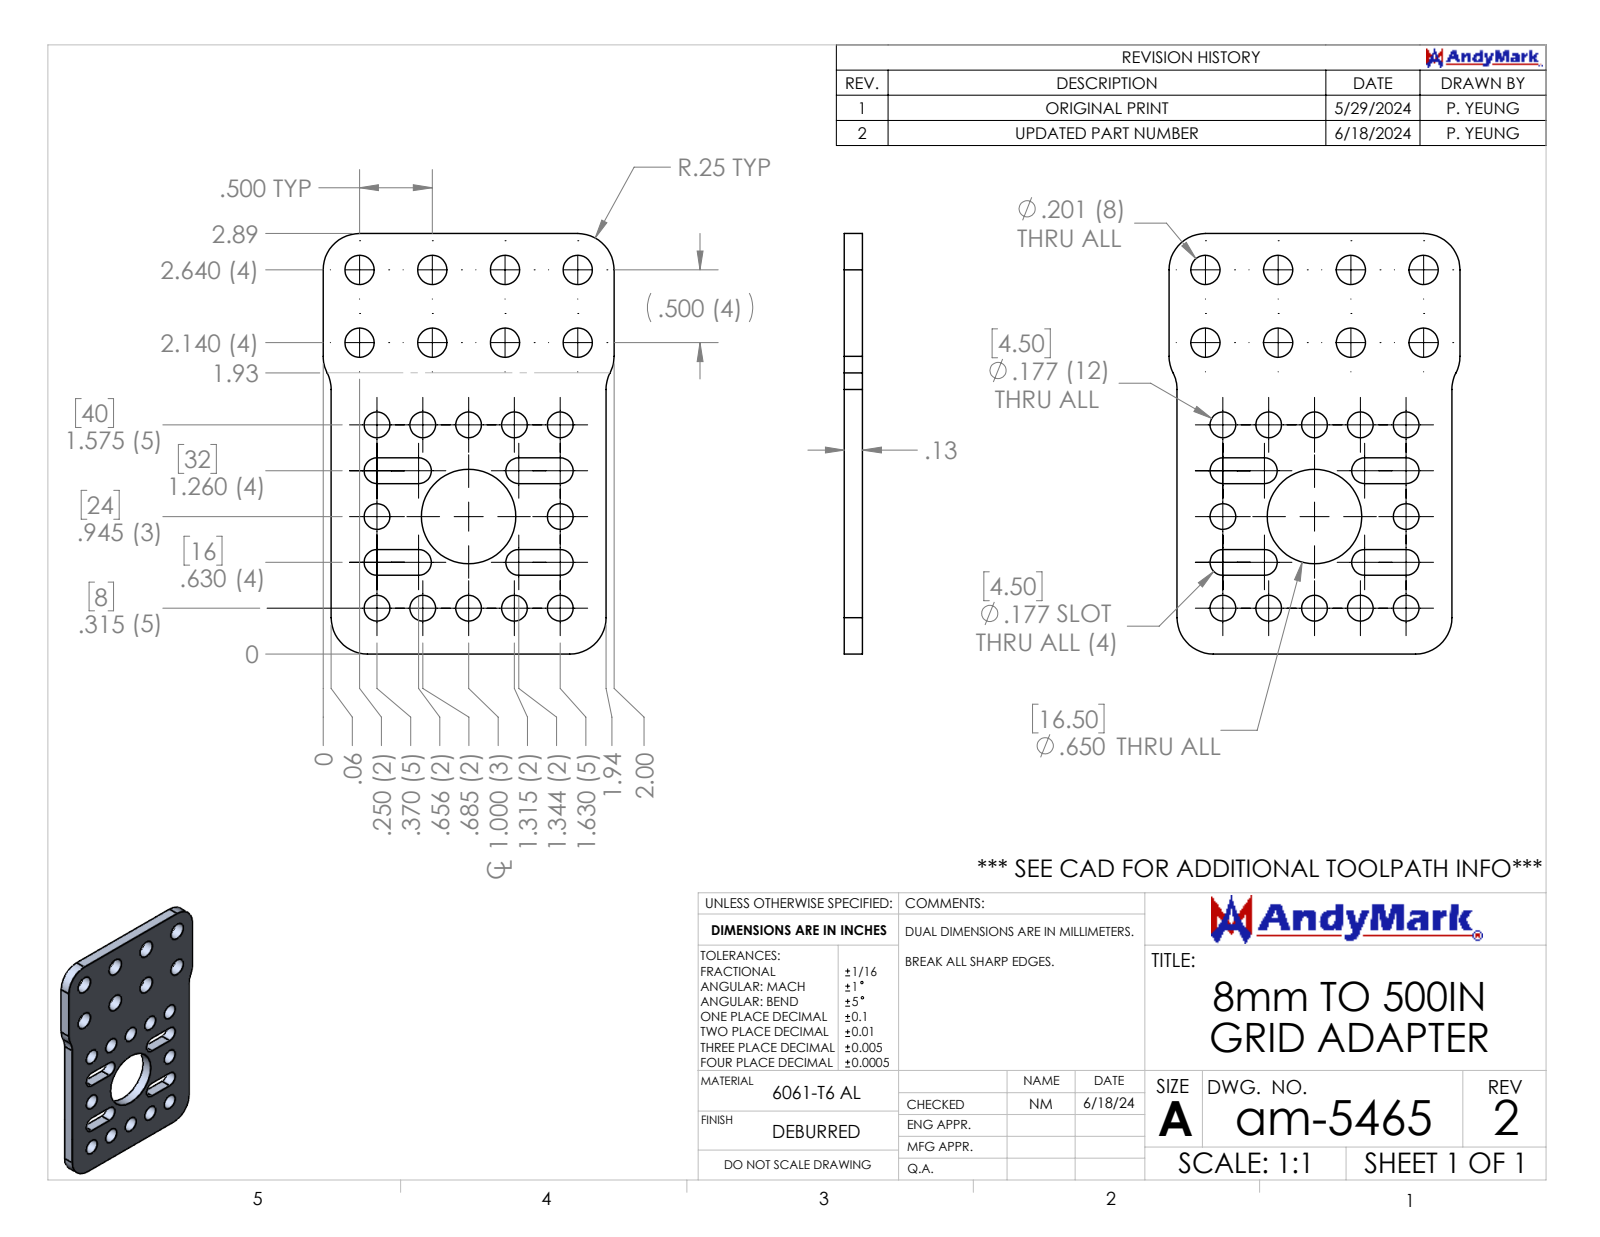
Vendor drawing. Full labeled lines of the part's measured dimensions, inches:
Part name (STEP PRODUCT): am-5439 8mm to 500IN Grid Adapter
STEP written by: SolidWorks 2024 (AUTOMOTIVE_DESIGN)
Units: inches
Bodies: 1 solid, 78 faces (16 planar, 62 cylindrical, 0 other)
Overall size (bounding box): 2.89 × 2 × 0.125
Volume: 0.541 in³ · Surface area: 12.1 in²
Round holes (diameter × count): ⌀0.177 ×12, ⌀0.201 ×8, ⌀0.65 ×1
Partial cylindrical surfaces — rounded edges, fillets, slot ends (radius × count): R0.089 ×8, R0.25 ×8
Main face-to-face distances: 0.125, 1.89, 2.89, 0.055, 1.945, 0.177, 0.63, 2, 0.541, 0.719
Hole centre spacings: 0.63, 0.5, 1.409, 0.315, 0.704, 0.891, 1.26, 1.298
